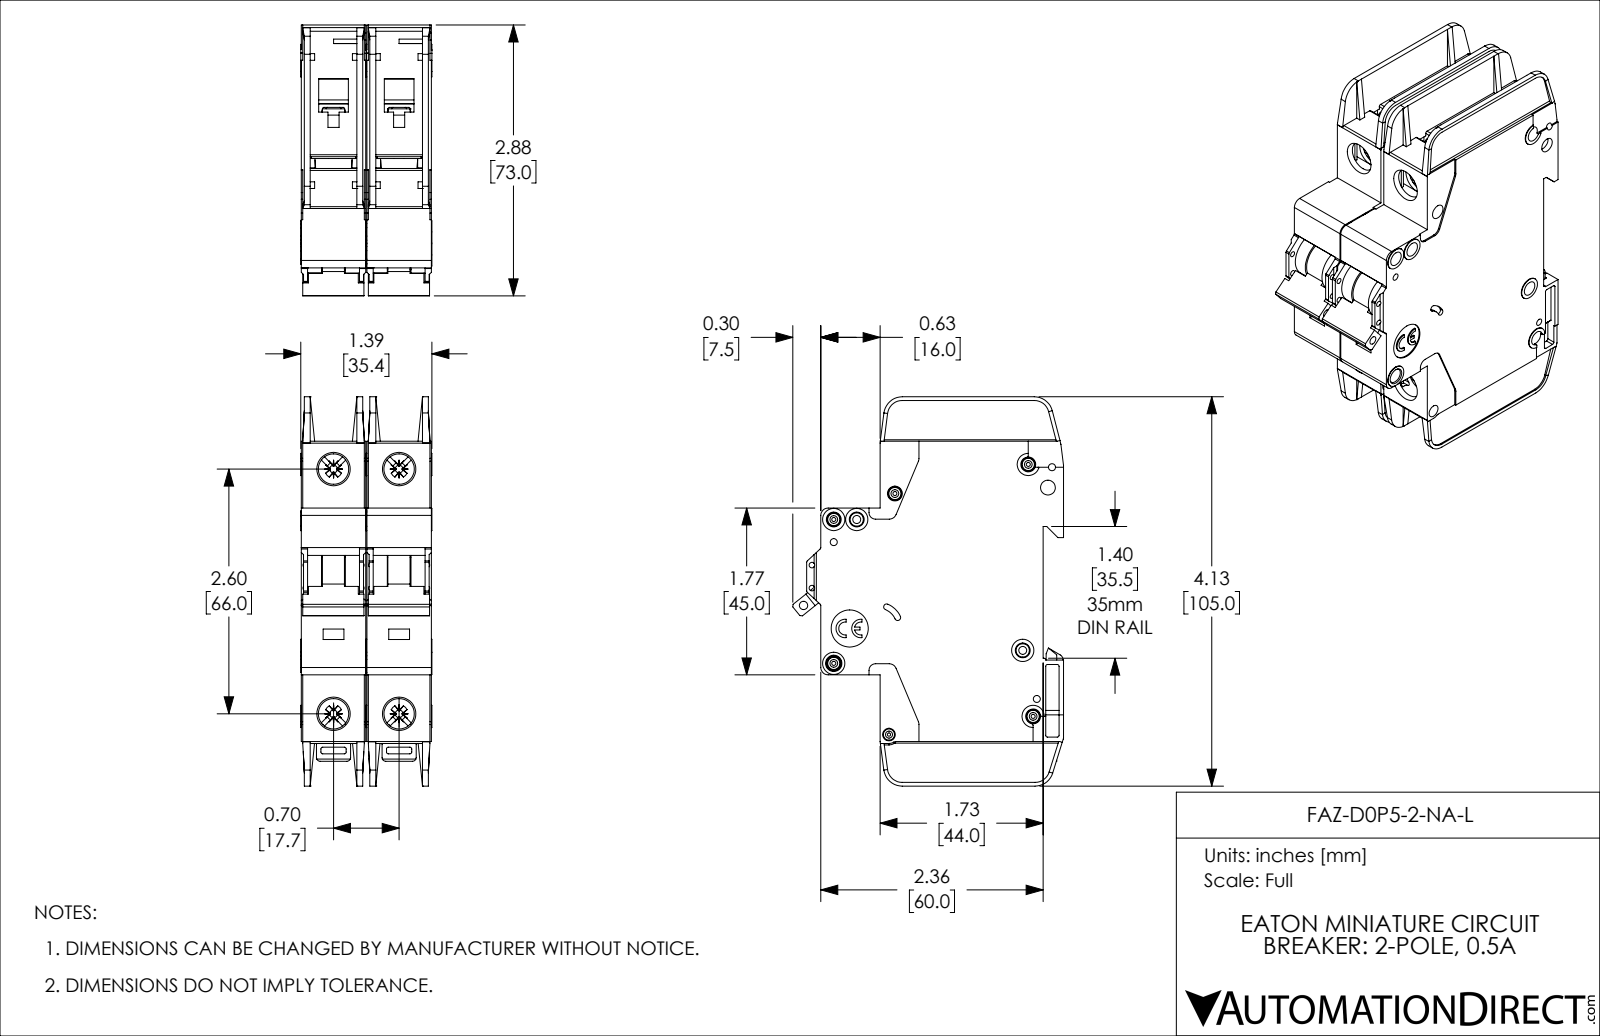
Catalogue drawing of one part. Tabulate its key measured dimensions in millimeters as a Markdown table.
| quantity | value |
| --- | --- |
| part name | FAZ-D0P5-2-NA-L |
| STEP written by | SolidWorks 2019 (AUTOMOTIVE_DESIGN) |
| units | millimeters |
| bodies | 2 solids, 2254 faces (1342 planar, 714 cylindrical, 198 other) |
| overall size | 105 × 73.1 × 35.4 |
| volume | 153 500 mm³ |
| surface area | 52 910 mm² |
| round holes (diameter × count) | 4 × 8, 1.1 × 5, 1.9 × 4, 8.2 × 4, 1.5 × 2, 2.2 × 2, 0.9 × 1, 2.3 × 1, 2.5 × 1, 3.4 × 1, 10 × 1 |
| round bosses / shafts (diameter × count) | 3.3 × 5, 6 × 4, 3 × 3, 2.5 × 2 |
| partial cylindrical surfaces (radius × count) | 0.5 × 57, 0.4 × 20, 1 × 14, 2 × 10, 1.1 × 8, 0.2 × 5, 5 × 5, 0.3 × 4 |
| main face-to-face distances | 17.7, 1.2, 17.4, 15, 2.4, 16.2, 13.8, 35.1, 18.9, 16.5 |
| hole center spacings | 6.2, 13.6, 17.7, 22.1, 66, 68.3, 4.8, 5.1 |
